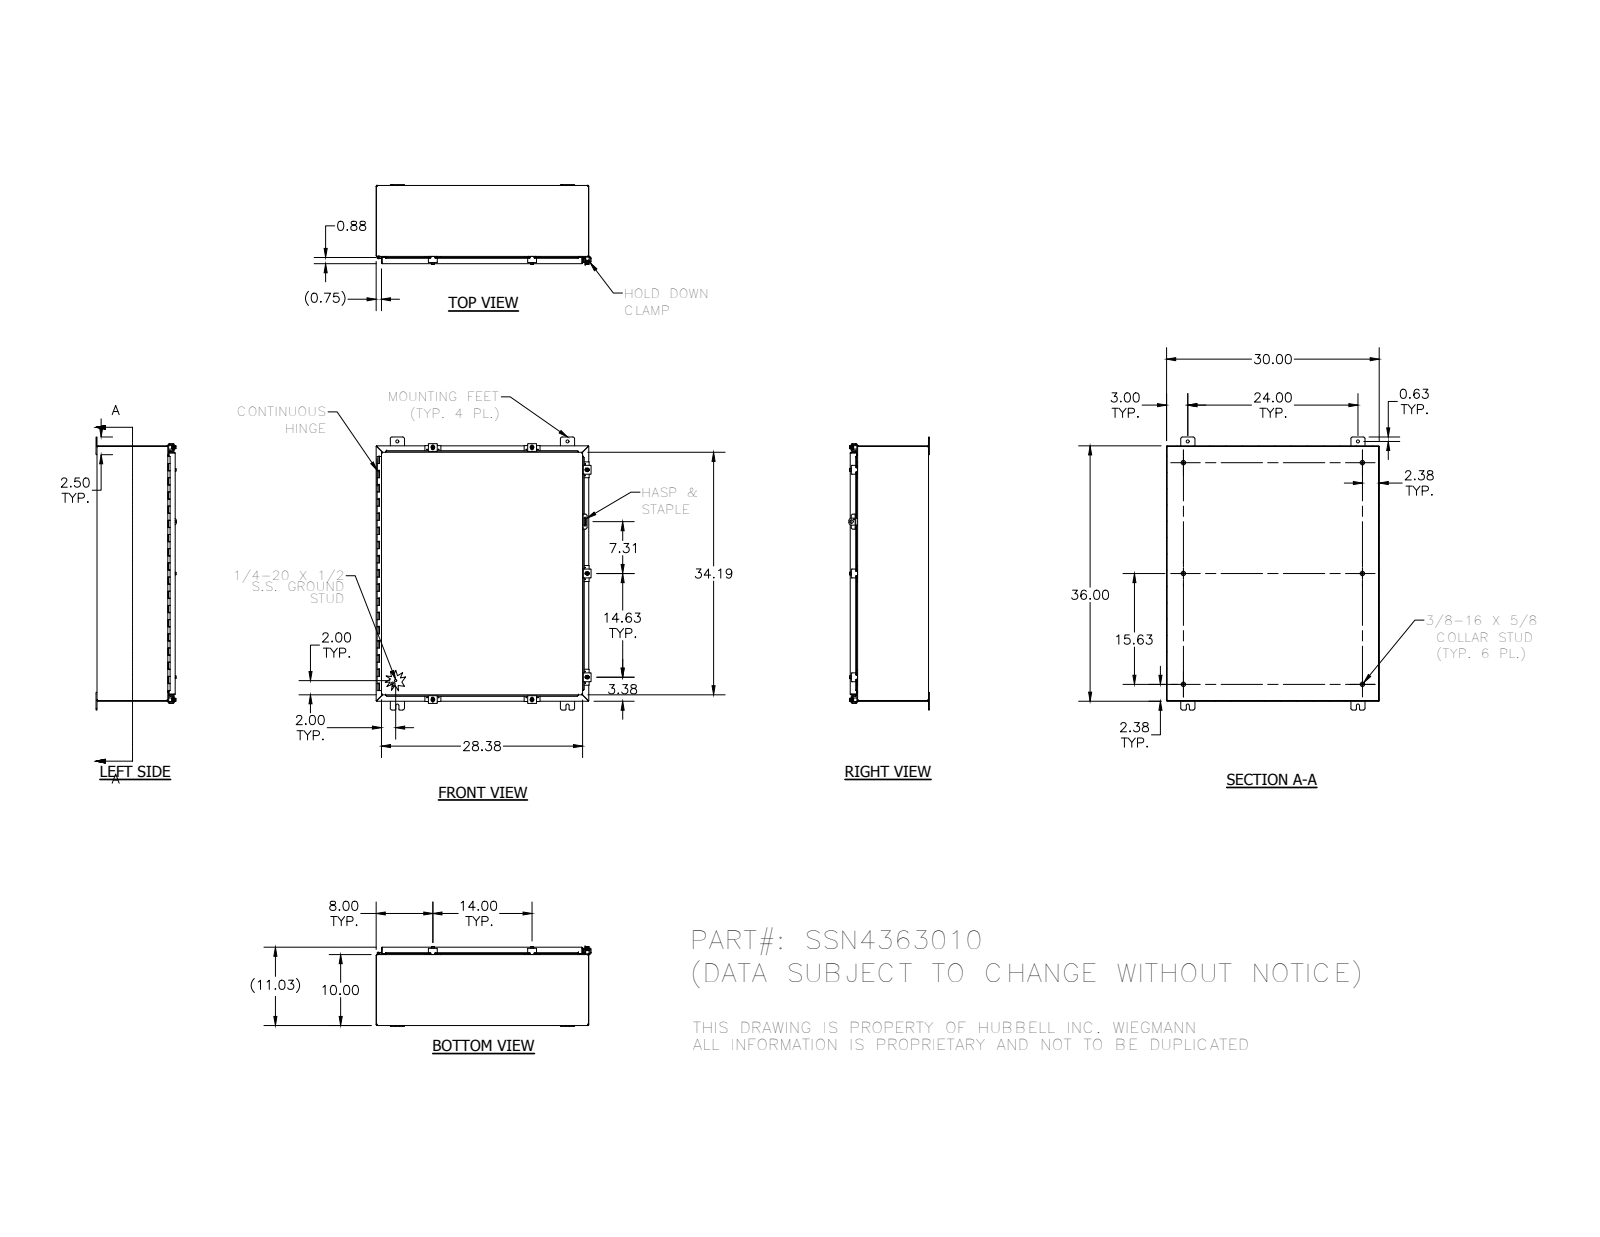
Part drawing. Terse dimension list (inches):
name: 38412; 328140; SSN43630LID; SSN4363010 (+8 more)
written by: SolidWorks 2014 (AUTOMOTIVE_DESIGN)
unit: in
bodies: 54 solids, 2204 faces (846 planar, 983 cylindrical, 375 other)
size: 38.5 × 30.311 × 11.355
volume: 302.7 in³; area: 7 995 in²
holes: 14× ⌀0.11, 7× ⌀0.211, 7× ⌀0.281, 7× ⌀0.3, 4× ⌀0.438, 1× ⌀0.125, 1× ⌀0.156, 1× ⌀0.5
bosses: 9× ⌀0.25, 7× ⌀0.52, 7× ⌀0.5, 7× ⌀0.35, 6× ⌀0.625, 6× ⌀0.33, 2× ⌀0.115, 1× ⌀0.337
rounds: 83× R0.03, 37× R0.125, 33× R0.25, 23× R0.031, 23× R0.105, 15× R0.062, 14× R0.141, 10× R0.1
face distances: 0.074, 10.959, 10.885, 11.033, 29.926, 35.926, 29.852, 30, 9.926, 1.033
hole spacings: 0.876, 35.298, 14, 1.625, 13.191, 14.816, 34.961, 34.998
